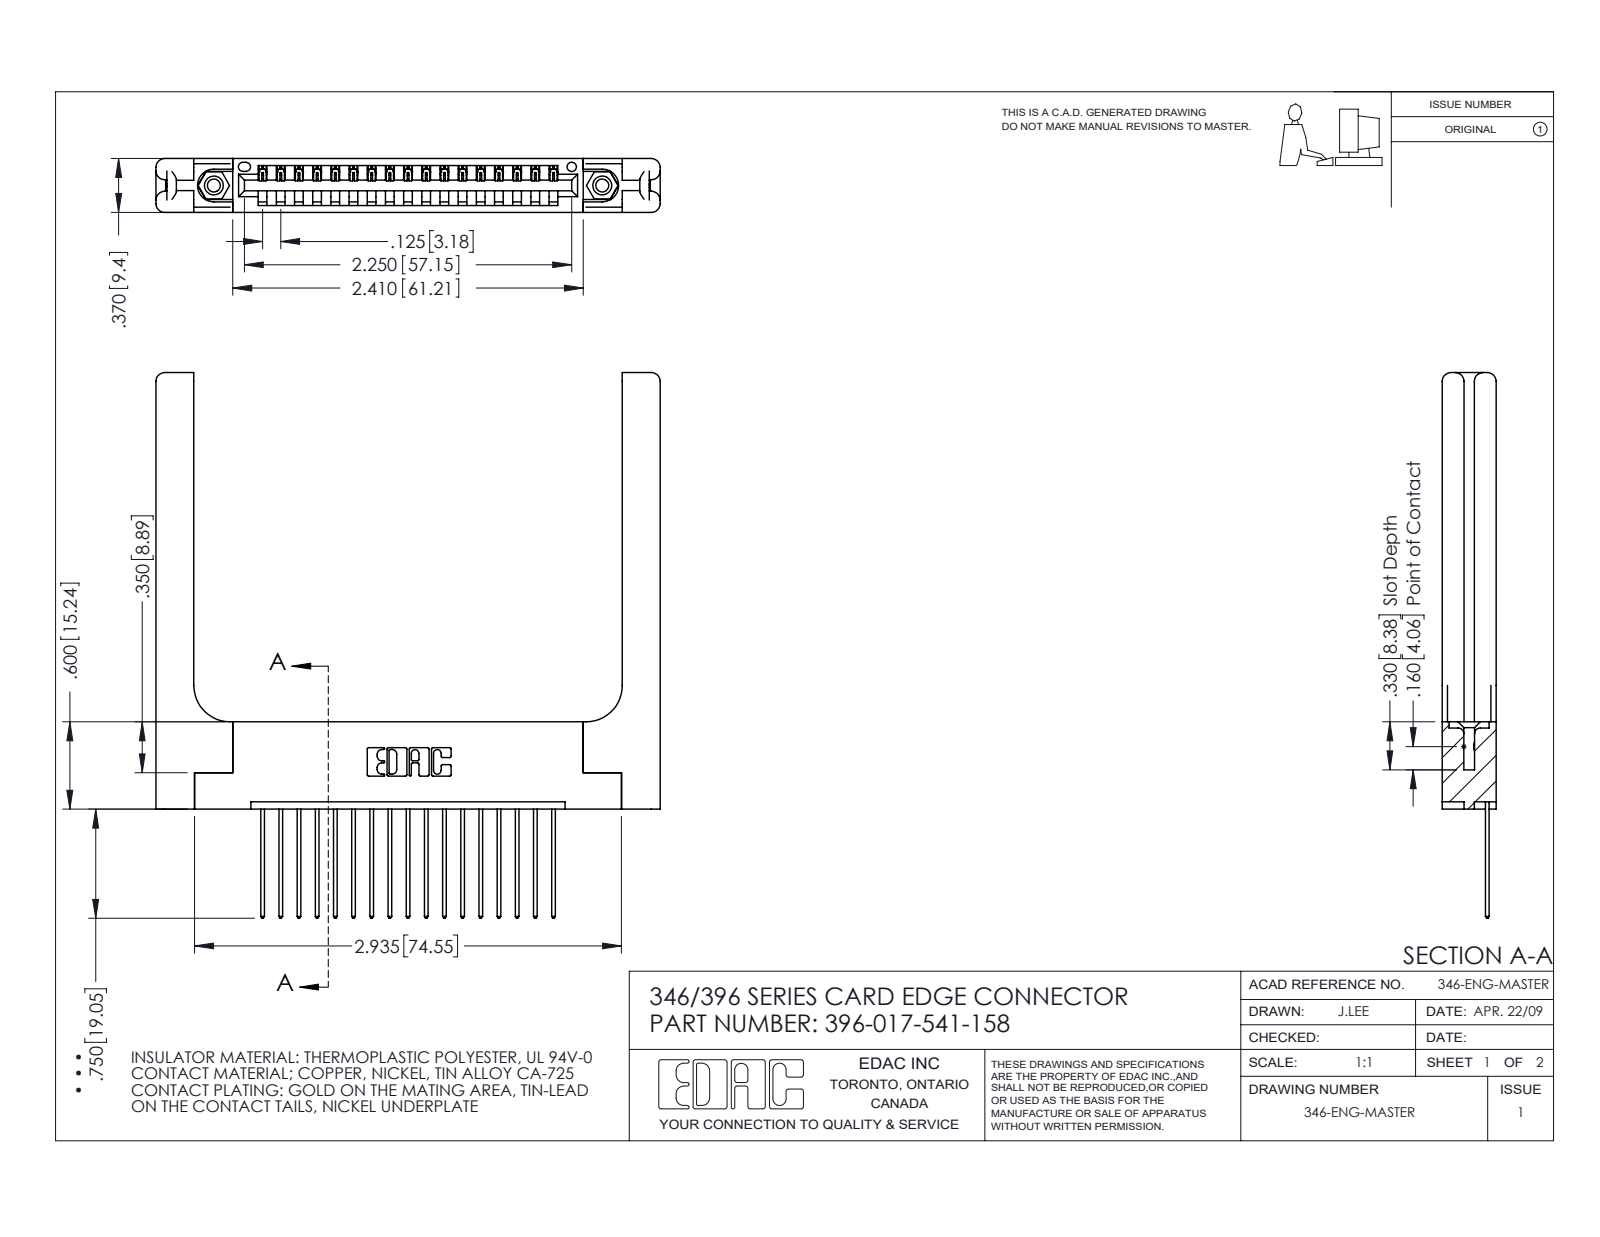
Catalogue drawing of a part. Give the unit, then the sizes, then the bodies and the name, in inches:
Units: inches
Overall size (bounding box): 3.75 × 3.466 × 0.37
Round holes (diameter × count): ⌀0.089 ×2, ⌀0.125 ×2, ⌀0.156 ×2, ⌀0.064 ×1
Round bosses / shafts (diameter × count): ⌀0.155 ×2
Partial cylindrical surfaces — rounded edges, fillets, slot ends (radius × count): R0.006 ×34, R0.01 ×34, R0.01 ×22, R0.06 ×16, R0.007 ×6, R0.031 ×6, R0.026 ×3, R0.03 ×2
Main face-to-face distances: 0.37, 0.072, 0.15, 0.048, 0.322, 0.148, 0.25, 0.298, 0.025, 0.102
Hole centre spacings: 0.246, 2.463, 2.67
Volume: 0.966 in³ · Surface area: 24.21 in²
Bodies: 22 solids, 1364 faces (904 planar, 400 cylindrical, 60 other)
Part name (STEP PRODUCT): 346 Part_Flush Mounting Lugs - 0.156 Dia-TH; 345-292-001_345-293-141; 396-017-541-158; 345-250-001_345-250-001-102 (+1 more)
STEP written by: SolidWorks 2016 (CONFIG_CONTROL_DESIGN)
